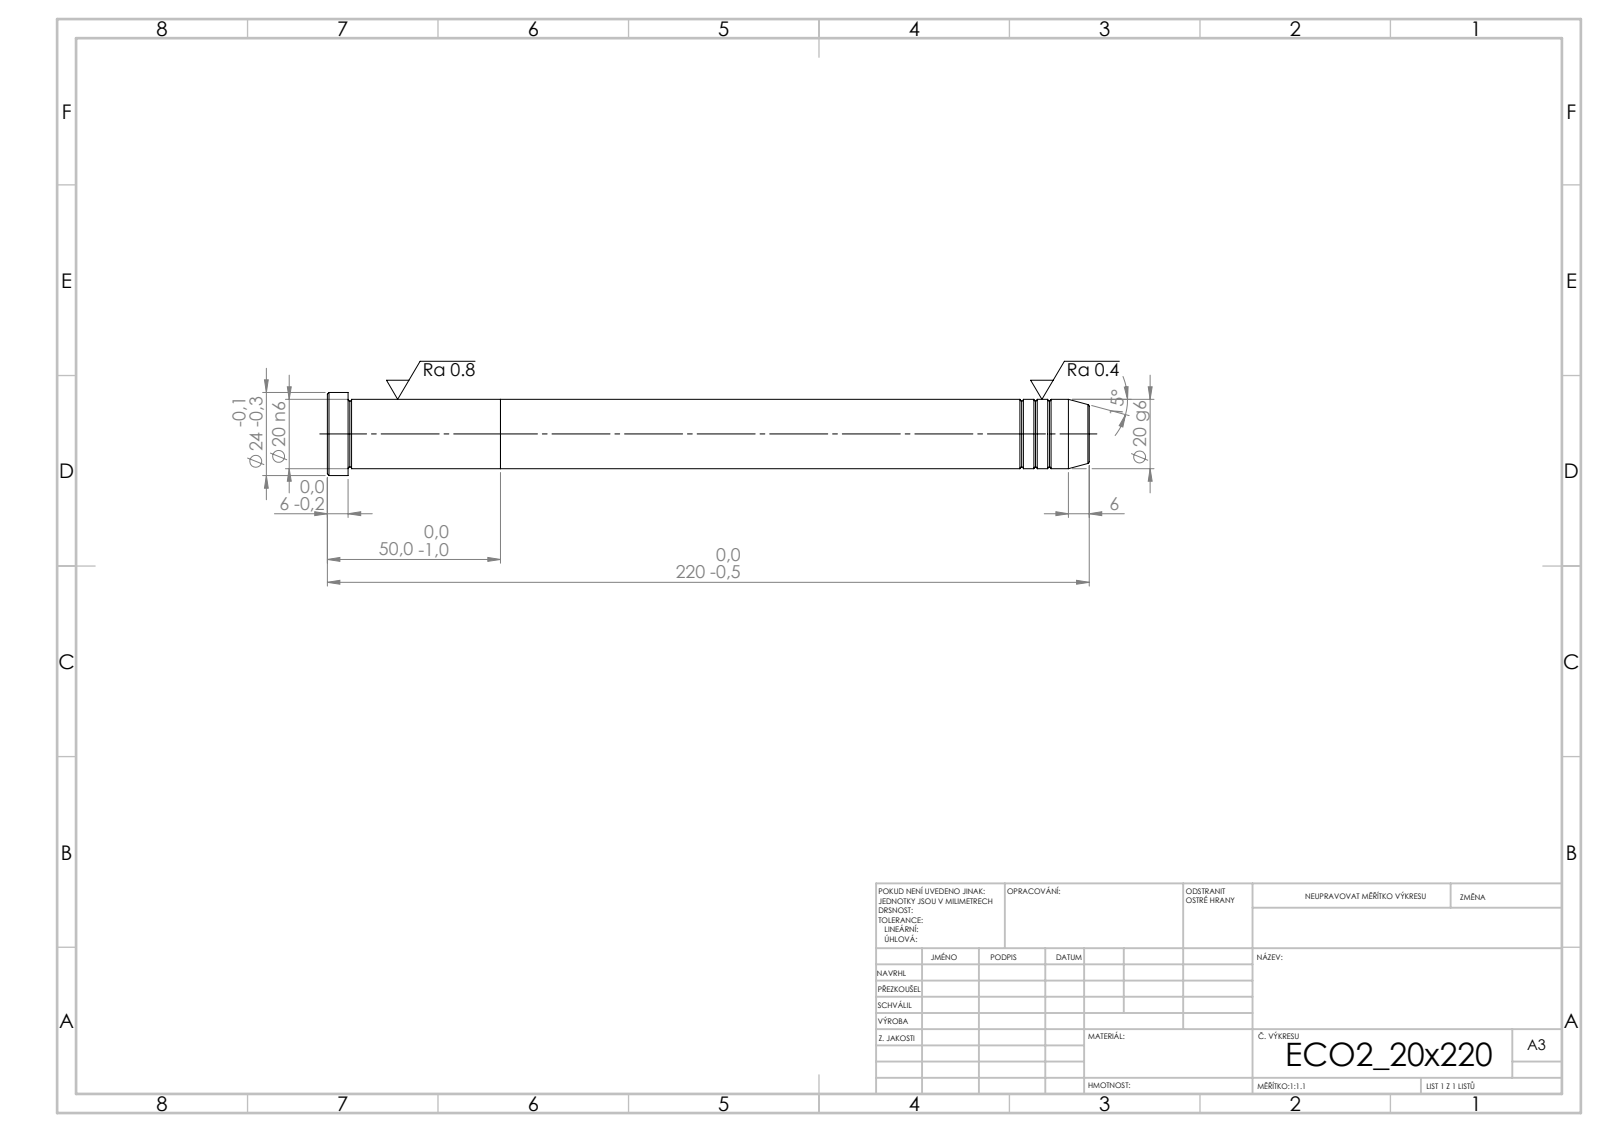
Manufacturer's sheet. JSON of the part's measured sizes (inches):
{"step_written_by": "SolidWorks 2019 (CONFIG_CONTROL_DESIGN)", "units": "inches", "bodies": {"solids": 2, "faces": 39, "planar": 5, "cylindrical": 12, "other": 22}, "overall_size": [8.661, 0.945, 0.945], "volume_in3": 4.244, "surface_area_in2": 23.91, "round_bosses_or_shafts": [[0.945, 1], [0.787, 1]], "face_to_face_distances": [1.969, 6.693, 8.661, 8.425, 1.732, 0.236]}
